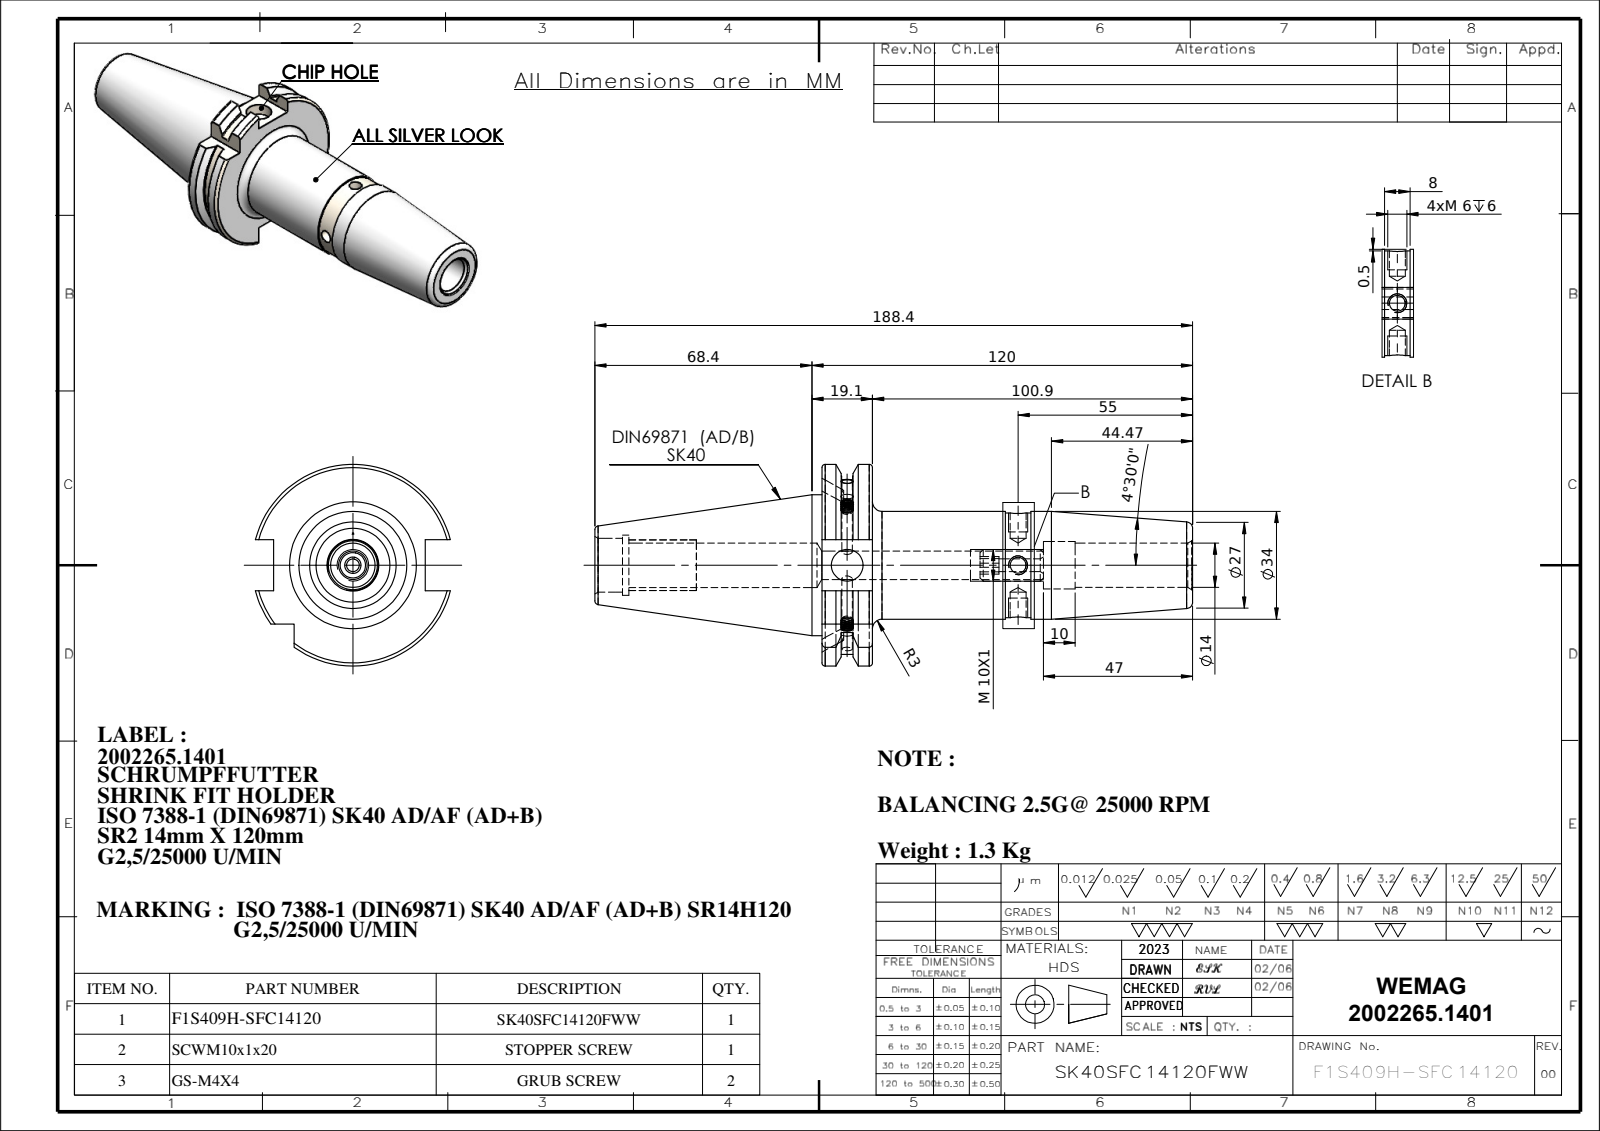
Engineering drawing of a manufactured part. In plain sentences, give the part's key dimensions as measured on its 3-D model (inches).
The part is named "SCWM10X1; GS-M4X4_DIN 913 - M4 x 4-N; SK40SFC14120FWW; 91406-SR14120". Its 3-D file was written by "SolidWorks 2018 (CONFIG_CONTROL_DESIGN)". It is 4 solids with 237 faces: 59 planar, 70 cylindrical and 108 other. Overall it measures 7.417 by 2.502 by 2.42 inches. Its volume is 10.56 cubic inches and its surface area 56.39 square inches. Round holes: 2 of diameter 0.197, 1 of diameter 0.13, 1 of diameter 0.157, 1 of diameter 0.354, 1 of diameter 0.394, 1 of diameter 0.551, 1 of diameter 0.551, 1 of diameter 0.59, 1 of diameter 0.669, 1 of diameter 0.748. Round bosses or shafts: 2 of diameter 0.157, 1 of diameter 1.75, 1 of diameter 1.339, 1 of diameter 1.299, 1 of diameter 0.394. Partial cylindrical surfaces (rounded edges, fillets, slot ends): 1 of radius 1.107, 1 of radius 1.251. The main face-to-face distances are 0.626, 4.598, 3.972, 0.634, 1.882, 2.748, 2.122, 1.85, 2.819, 3.445. The hole center spacings are 2.12.
